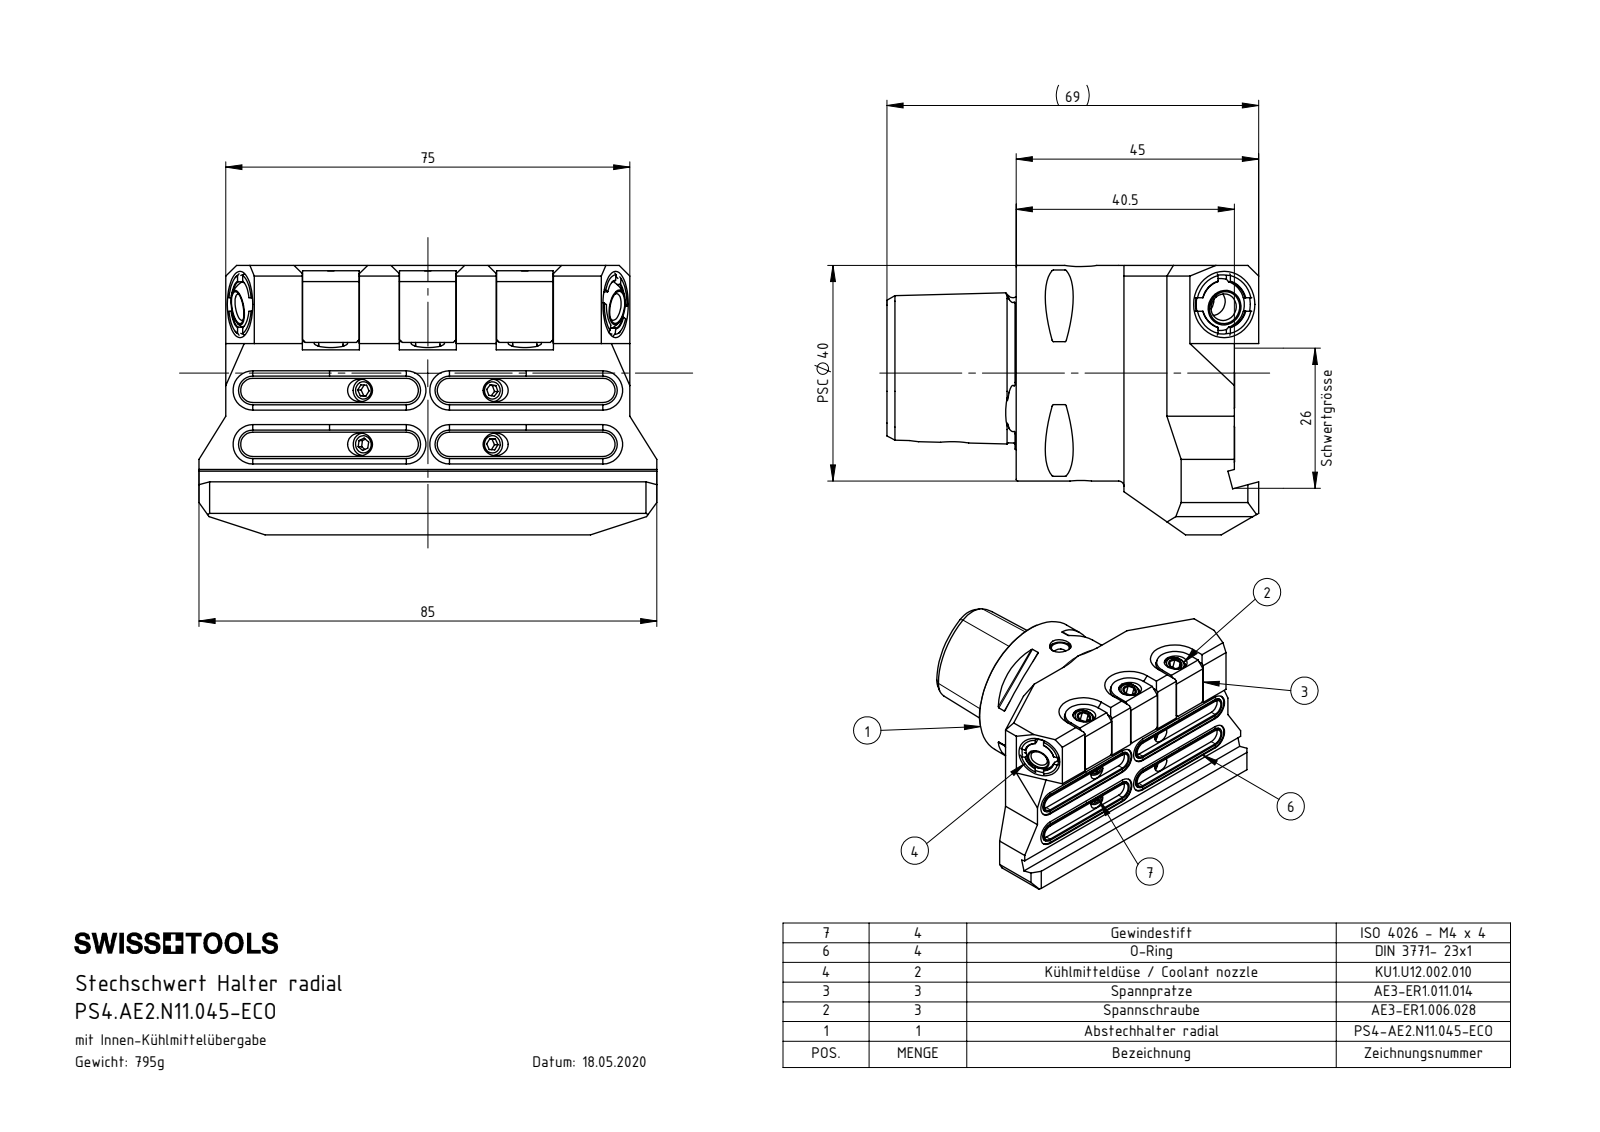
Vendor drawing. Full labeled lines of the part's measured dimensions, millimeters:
Part name (STEP PRODUCT): KU1-U12.002.010_A; PS4-AE2.N11.045-ECO_A; S4-.E2.N11.045-ECO; KU1-U12.002.010 (+7 more)
STEP written by: SolidWorks 2017 (AUTOMOTIVE_DESIGN)
Units: millimetres
Bodies: 23 solids, 764 faces (273 planar, 207 cylindrical, 284 other)
Overall size (bounding box): 85 × 69.09 × 50
Volume: 101 427 mm³ · Surface area: 32 504 mm²
Round holes (diameter × count): ⌀5 ×8, ⌀3.3 ×4, ⌀4.2 ×4, ⌀3 ×3, ⌀5.5 ×3, ⌀6.2 ×3, ⌀10 ×2, ⌀11 ×2, ⌀4 ×1, ⌀4.6 ×1, ⌀12.5 ×1, ⌀18 ×1
Round bosses / shafts (diameter × count): ⌀6 ×4, ⌀4 ×4, ⌀1 ×4, ⌀4.5 ×3, ⌀12 ×2, ⌀40 ×1
Partial cylindrical surfaces — rounded edges, fillets, slot ends (radius × count): R0.3 ×8, R2.25 ×8, R2.65 ×8, R3.65 ×8, R5.25 ×3, R5.3 ×3, R4.4 ×2, R3 ×1
Main face-to-face distances: 4.5, 18, 1.5, 6, 19, 20.5, 25, 19.65, 0.65, 0.85
Hole centre spacings: 10, 18, 23.5, 36
